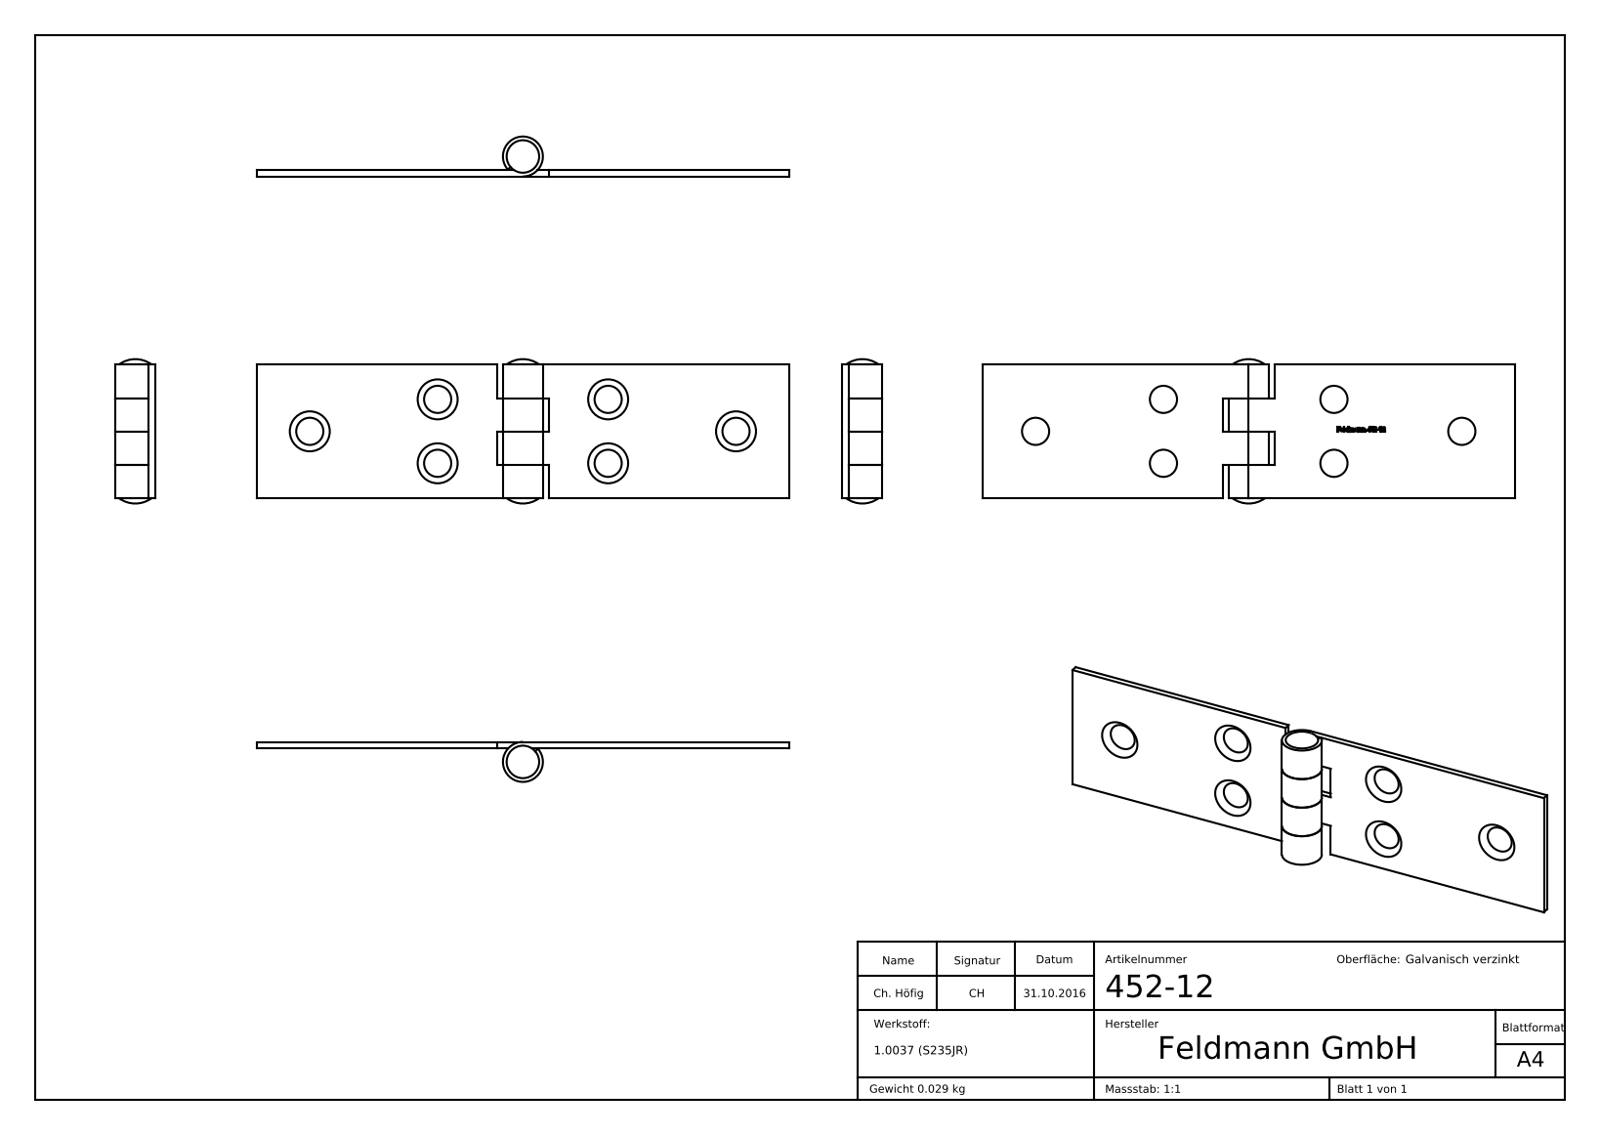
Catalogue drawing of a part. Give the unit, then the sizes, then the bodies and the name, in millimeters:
Units: millimetres
Overall size (bounding box): 100 × 27.1 × 7.5
Round holes (diameter × count): ⌀5.1 ×1
Round bosses / shafts (diameter × count): ⌀7.5 ×1
Partial cylindrical surfaces — rounded edges, fillets, slot ends (radius × count): R0.1 ×48
Main face-to-face distances: 1.2, 6.25, 12.5, 25, 18.75, 100, 45.2, 54.8, 6.3, 12.55
Volume: 3 682 mm³ · Surface area: 6 419 mm²
Bodies: 3 solids, 165 faces (26 planar, 69 cylindrical, 70 other)
Part name (STEP PRODUCT): 452-12 Teil2_Keyshot; 452-12 Teil3; 452-12 Teil1_Keyshot; 452-12 Teil1 (+2 more)
STEP written by: SolidWorks 2018 (CONFIG_CONTROL_DESIGN)
